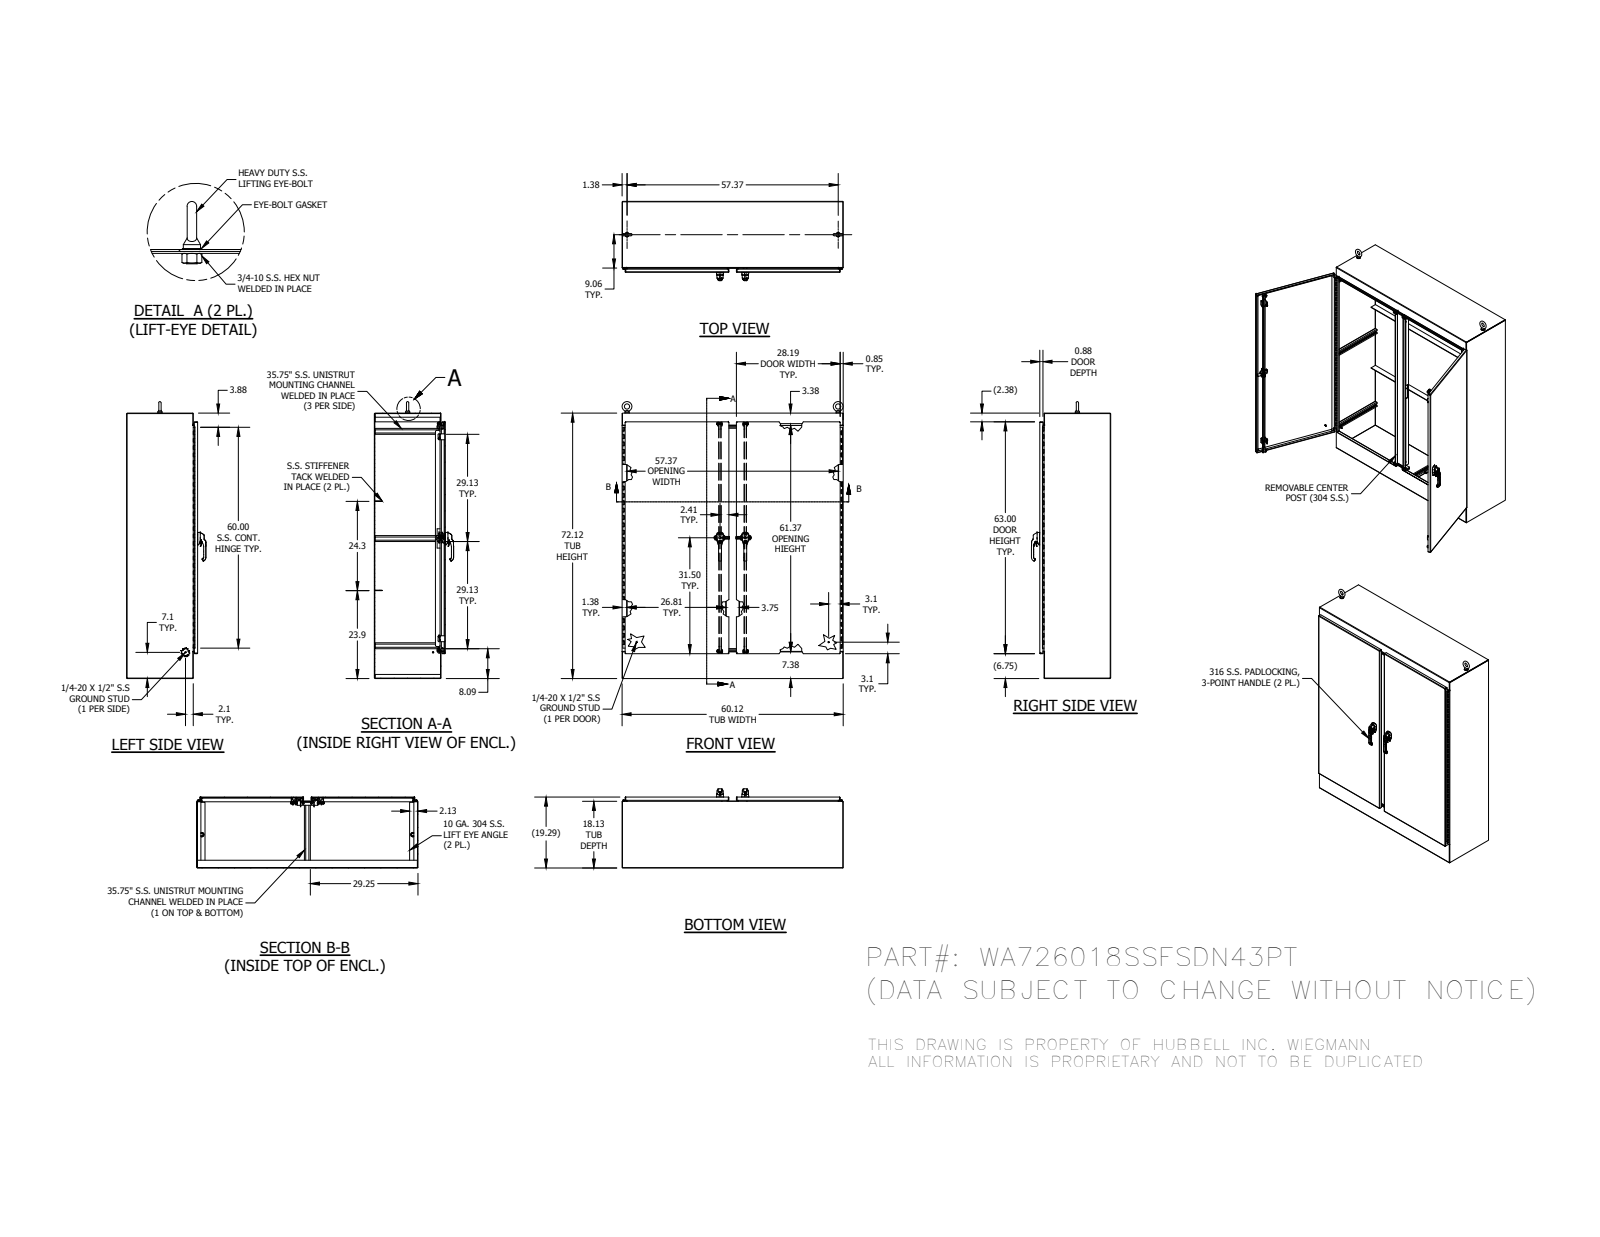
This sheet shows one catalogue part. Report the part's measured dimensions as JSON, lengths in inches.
{"part_name": "1225-05; D125B_10_5; 328131L-60; 328131T-60 (+8 more)", "step_written_by": "SolidWorks 2014 (AUTOMOTIVE_DESIGN)", "units": "inches", "bodies": {"solids": 133, "faces": 7024, "planar": 2638, "cylindrical": 2690, "other": 1696}, "overall_size": [75.248, 60.125, 21.541], "volume_in3": 2048, "surface_area_in2": 33412, "round_holes": [[0.262, 16], [0.375, 16], [0.187, 8], [0.213, 6], [0.281, 6], [0.25, 5], [0.196, 4], [0.241, 4], [0.252, 4], [0.281, 4], [0.315, 4], [0.4, 4]], "round_bosses_or_shafts": [[0.25, 7], [0.533, 6], [0.236, 6], [1, 5], [0.563, 4], [0.531, 4], [0.5, 4], [0.438, 4]], "partial_cylinders_radius": [[0.02, 352], [0.012, 214], [0.019, 44], [0.125, 44], [0.05, 34], [0.079, 28], [0.025, 24], [0.059, 24]], "face_to_face_distances": [0.125, 0.125, 19.167, 60, 18, 1.167, 72, 19.165, 19.04, 19.042], "hole_center_spacings": [54.49, 55.24, 20, 0.38, 0.38, 6.667, 0.76, 13.333]}
